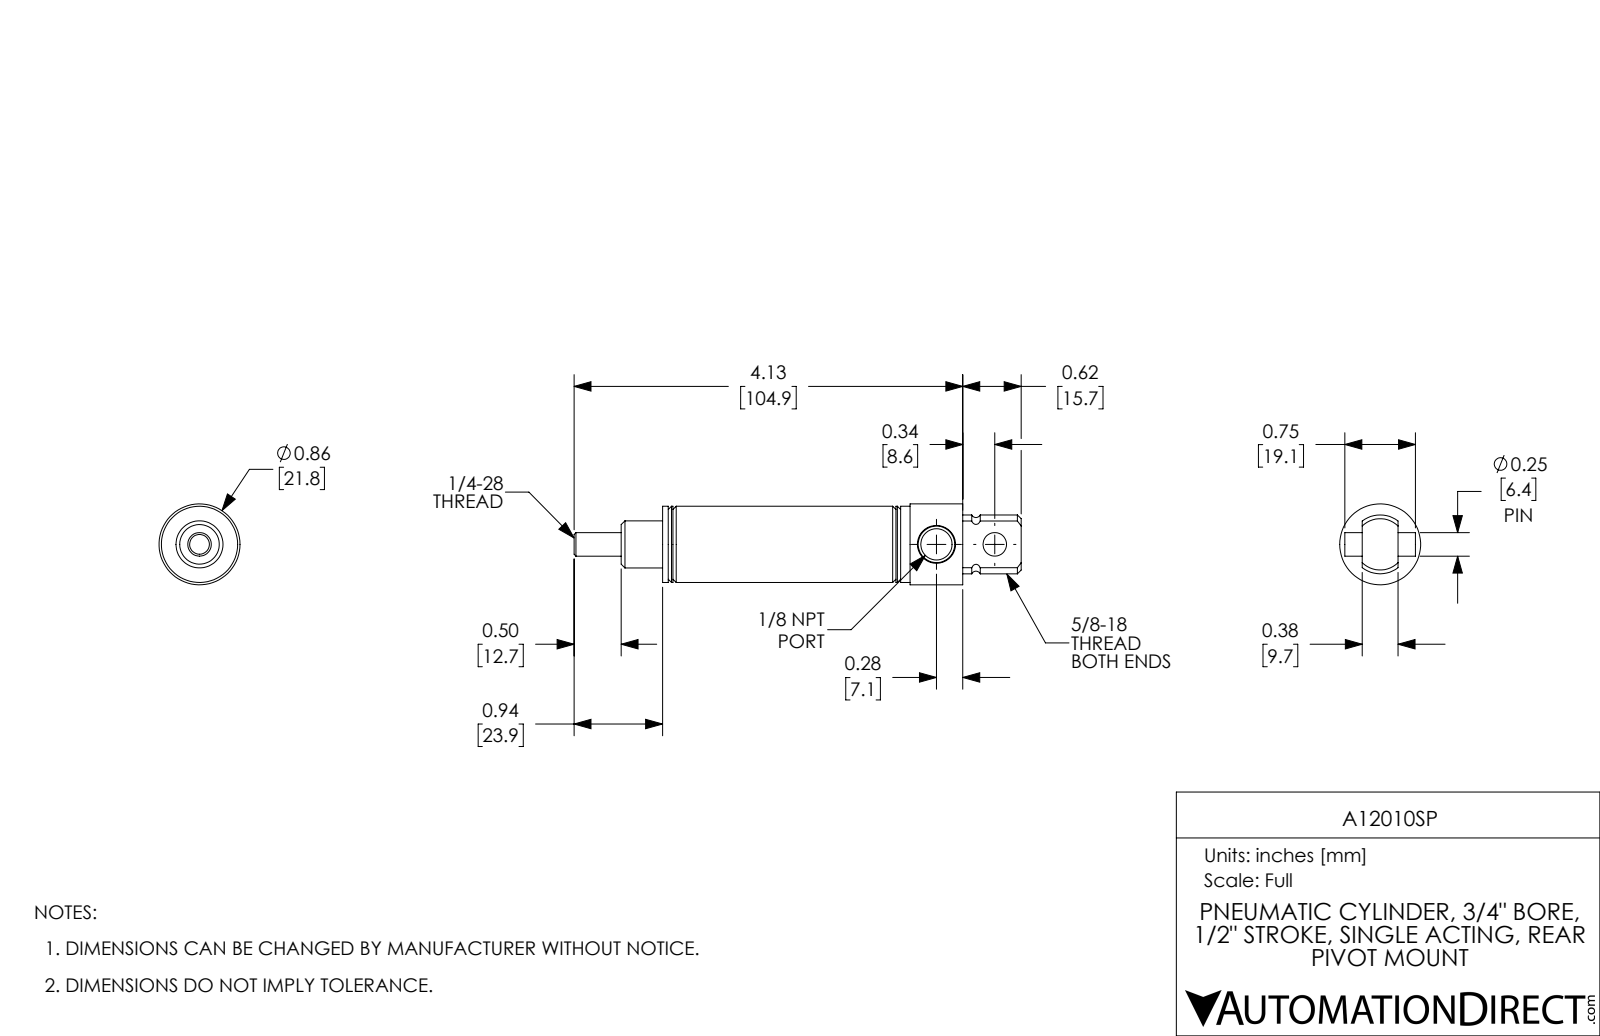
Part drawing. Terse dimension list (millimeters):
name: A12010SP-Pin; A12010SP-Rod; A12010SP-MainBody; A12010SP
written by: SolidWorks 2017 (AUTOMOTIVE_DESIGN)
unit: mm
bodies: 3 solids, 73 faces (19 planar, 32 cylindrical, 22 other)
size: 120.7 × 21.8 × 21.8
volume: 24 480 mm³; area: 14 550 mm²
holes: 2× ⌀6.4, 1× ⌀8.4, 1× ⌀19.1
bosses: 1× ⌀21.8, 1× ⌀20.6, 1× ⌀12.7
rounds: 1× R8
face distances: 21.5, 59.6, 12.7, 25.4, 38.1, 34.2, 81, 46.9, 9.7, 15.7
hole spacings: 15.7
